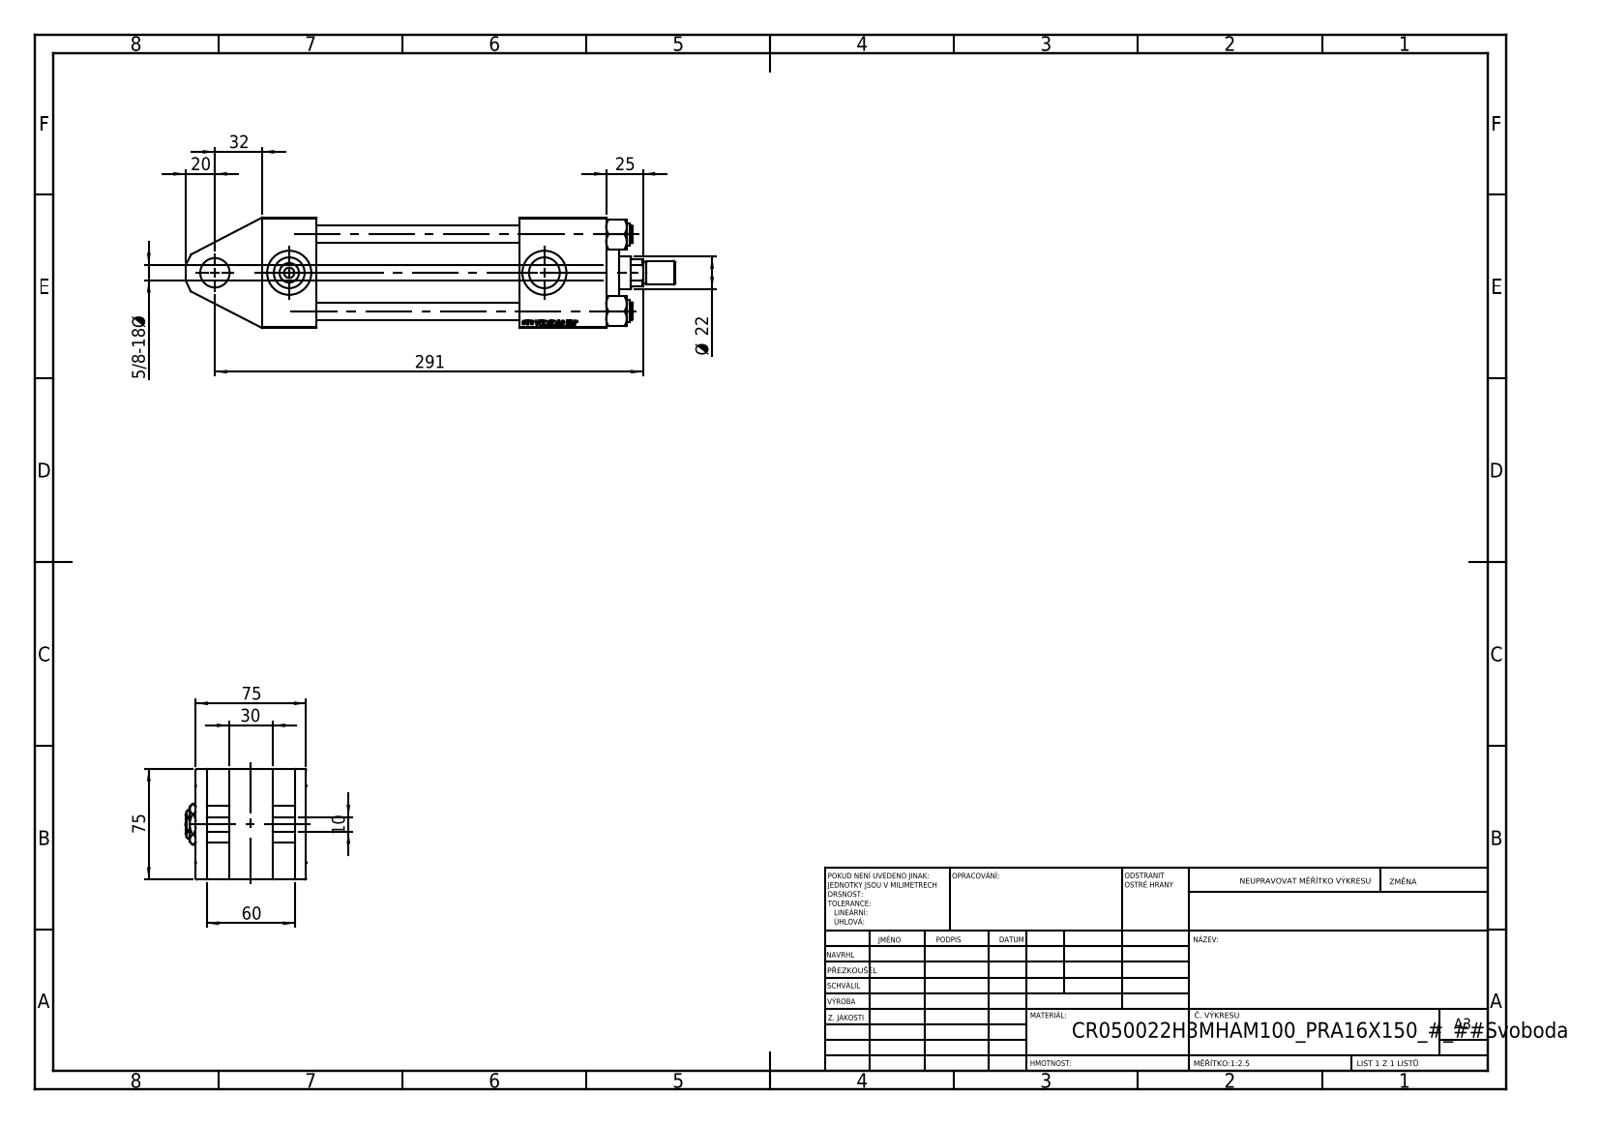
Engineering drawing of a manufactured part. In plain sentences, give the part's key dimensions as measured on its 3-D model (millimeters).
The part is named "Zatka_pro_OIL_PORT; NUT_M5_H; ROD_END_AH; V215CR_VCP_H (+3 more)". Its 3-D file was written by "SolidWorks 2019 (CONFIG_CONTROL_DESIGN)". It is 14 solids with 1243 faces: 569 planar, 98 cylindrical and 576 other. Overall it measures 333 by 82.27 by 75 millimeters. Its volume is 839 430 cubic millimeters and its surface area 213 226 square millimeters. Round holes: 4 of diameter 12, 2 of diameter 7, 2 of diameter 20.96, 2 of diameter 30, 1 of diameter 10.5, 1 of diameter 20, 1 of diameter 22, 1 of diameter 25, 1 of diameter 41, 1 of diameter 50, 1 of diameter 53. Round bosses or shafts: 4 of diameter 15, 1 of diameter 56, 1 of diameter 34, 1 of diameter 16, 1 of diameter 14. Partial cylindrical surfaces (rounded edges, fillets, slot ends): 1 of radius 10.5. The main face-to-face distances are 75, 197, 7.5, 67.5, 45, 22.5, 52.5, 15, 175, 59. The hole center spacings are 36.98, 52.3, 73.96, 50.5, 173.5, 224.
